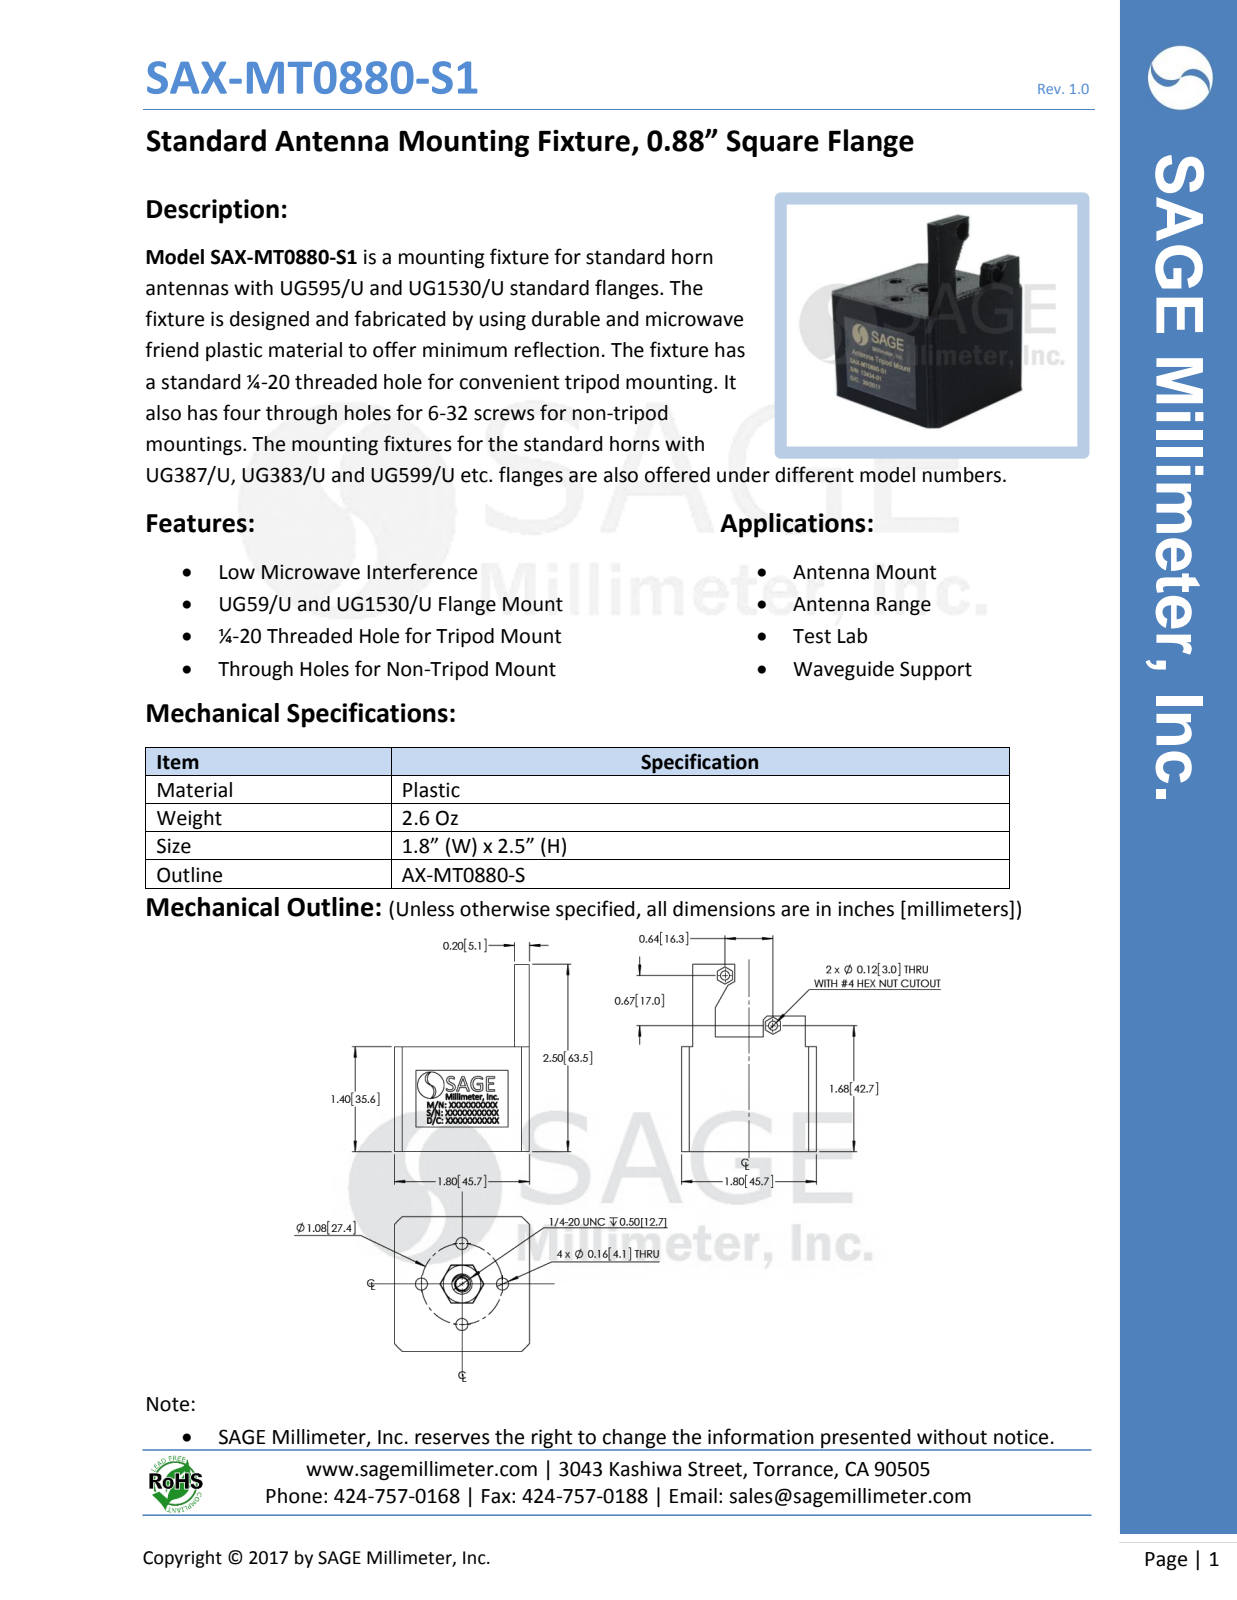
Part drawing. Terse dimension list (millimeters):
name: SAX-MT0880-S1
written by: SolidWorks 2021 (CONFIG_CONTROL_DESIGN)
unit: mm
bodies: 3 solids, 179 faces (72 planar, 40 cylindrical, 67 other)
size: 63.5 × 45.7 × 45.7
volume: 73 990 mm³; area: 14 020 mm²
holes: 4× ⌀4.3, 2× ⌀2.2, 2× ⌀2.8, 2× ⌀3, 1× ⌀10.2
bosses: 1× ⌀9.5
rounds: 1× R30.5
face distances: 45.7, 35.6, 5.1, 40.6, 3.8, 41.9, 3.3, 24.6, 38.9, 30.5
hole spacings: 13.7, 19.4, 27.4, 23.5
